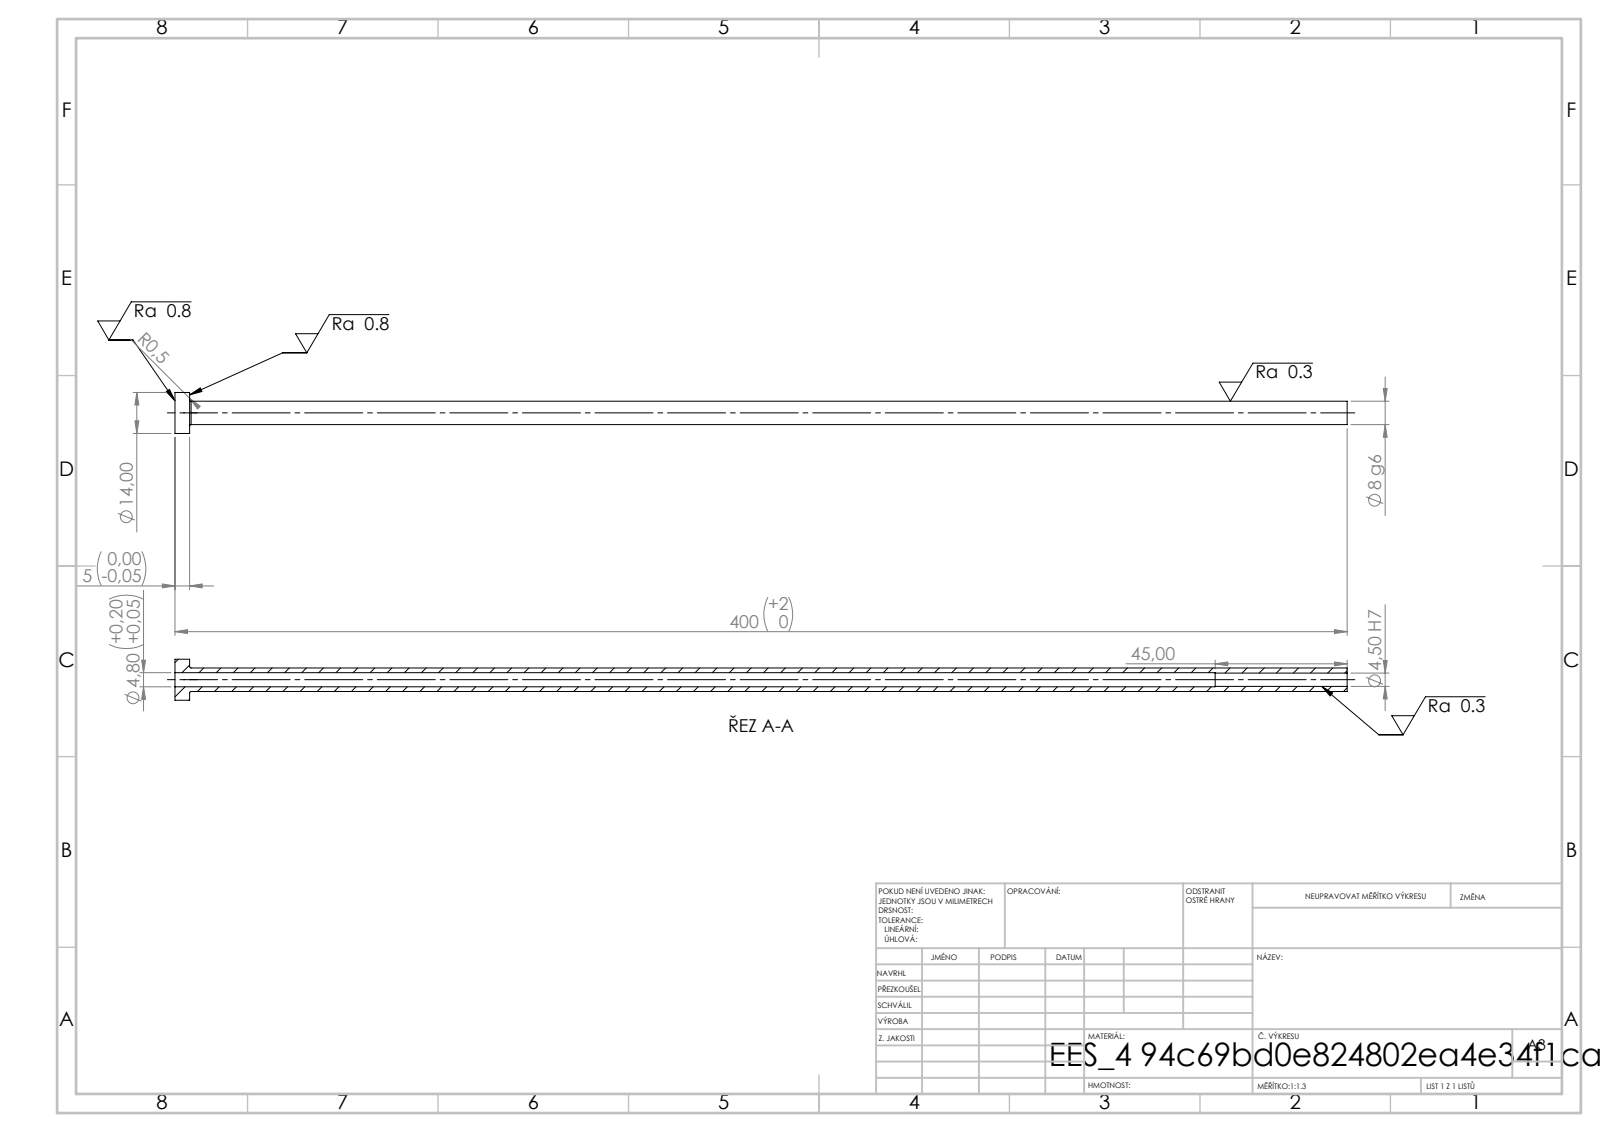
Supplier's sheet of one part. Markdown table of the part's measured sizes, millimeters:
| quantity | value |
| --- | --- |
| STEP written by | SolidWorks 2019 (CONFIG_CONTROL_DESIGN) |
| units | millimeters |
| bodies | 1 solid, 14 faces (4 planar, 8 cylindrical, 2 other) |
| overall size | 400 × 14 × 14 |
| volume | 13 486 mm³ |
| surface area | 16 408 mm² |
| round holes (diameter × count) | 4.5 × 1, 4.8 × 1 |
| round bosses / shafts (diameter × count) | 14 × 1, 8 × 1 |
| main face-to-face distances | 5, 400, 395, 355, 350, 45 |
